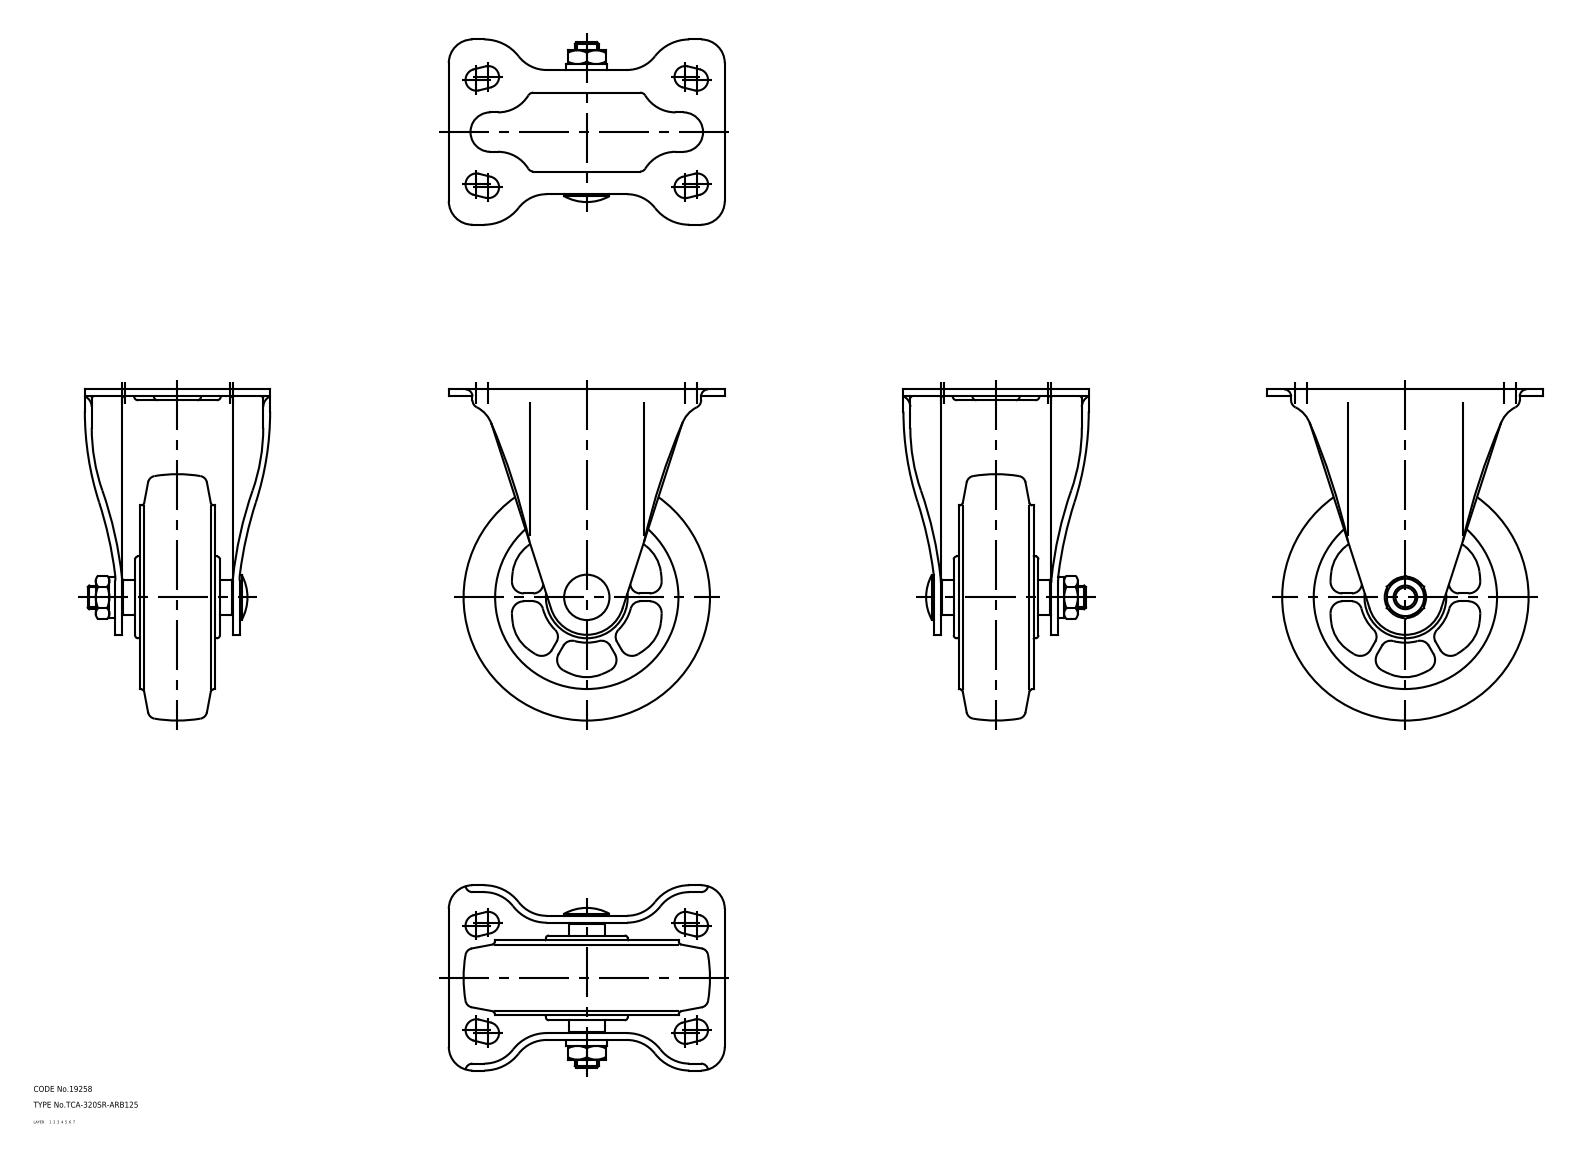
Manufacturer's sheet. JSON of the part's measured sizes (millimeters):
{"part_name": "wheel; axle; 320SR_ARB125_1204_36", "step_written_by": "CADfix (AUTOMOTIVE_DESIGN)", "units": "millimeters", "bodies": {"solids": 3, "faces": 280, "planar": 0, "cylindrical": 0, "other": 280}, "overall_size": [168, 140, 94], "volume_mm3": 430428, "surface_area_mm2": 113876}
